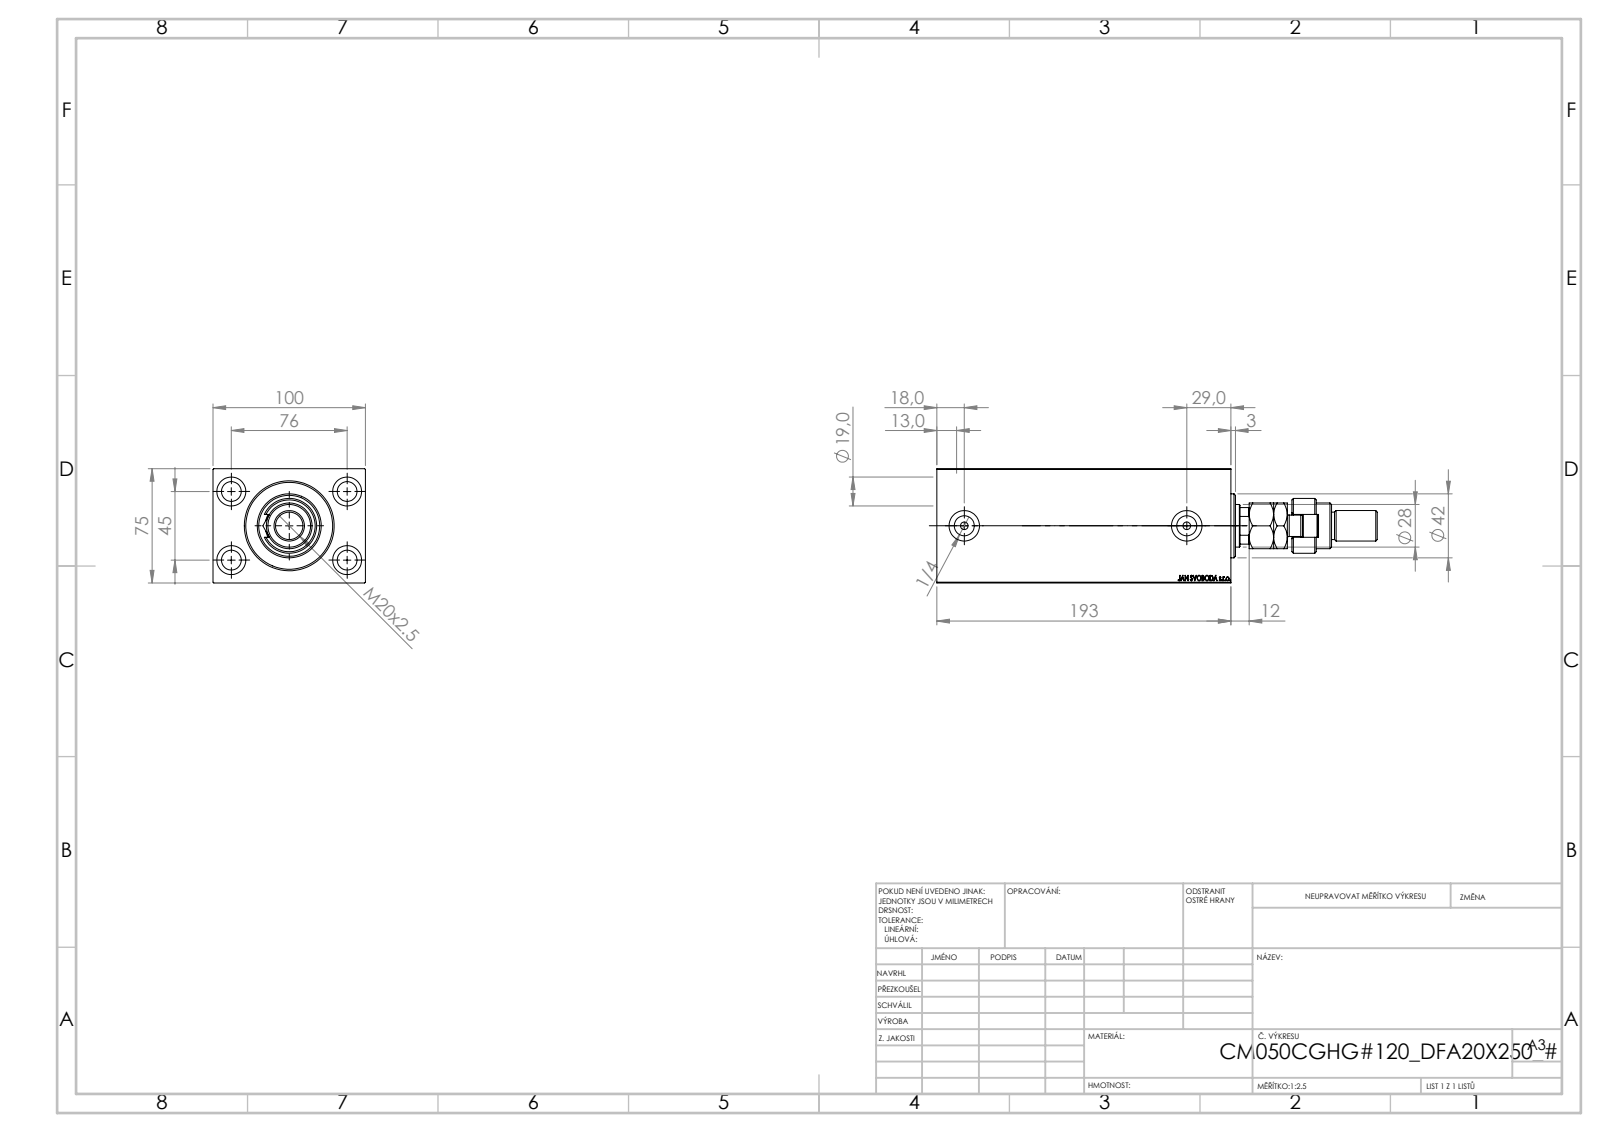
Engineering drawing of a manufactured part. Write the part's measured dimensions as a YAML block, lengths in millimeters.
part_name: "V450CM_C_VCP; V450CM_C_Body; MFA; FEMALE_PART_FOR_DFA (+1 more)"
step_written_by: "SolidWorks 2019 (CONFIG_CONTROL_DESIGN)"
units: millimeters
bodies: {solids: 5, faces: 950, planar: 437, cylindrical: 75, other: 438}
overall_size: [289, 100, 75]
volume: 1214000
surface_area: 193904
round_holes:
  - {diameter: 13, count: 4}
  - {diameter: 19, count: 4}
  - {diameter: 5, count: 2}
  - {diameter: 13.16, count: 2}
  - {diameter: 20, count: 2}
  - {diameter: 18.5, count: 1}
  - {diameter: 28, count: 1}
  - {diameter: 31.5, count: 1}
  - {diameter: 50, count: 1}
  - {diameter: 52, count: 1}
  - {diameter: 57, count: 1}
round_bosses_or_shafts:
  - {diameter: 42, count: 1}
  - {diameter: 36, count: 1}
  - {diameter: 30, count: 1}
  - {diameter: 22, count: 1}
  - {diameter: 20, count: 1}
  - {diameter: 18, count: 1}
  - {diameter: 14, count: 1}
partial_cylinders:
  - {radius: 7.5, count: 1}
  - {radius: 12, count: 1}
  - {radius: 13.5, count: 1}
face_to_face_distances: [75, 100, 193, 179, 14, 30, 29.3, 149.7, 163.7, 13]
hole_center_spacings: [44.16, 45, 76, 88.32, 146]
